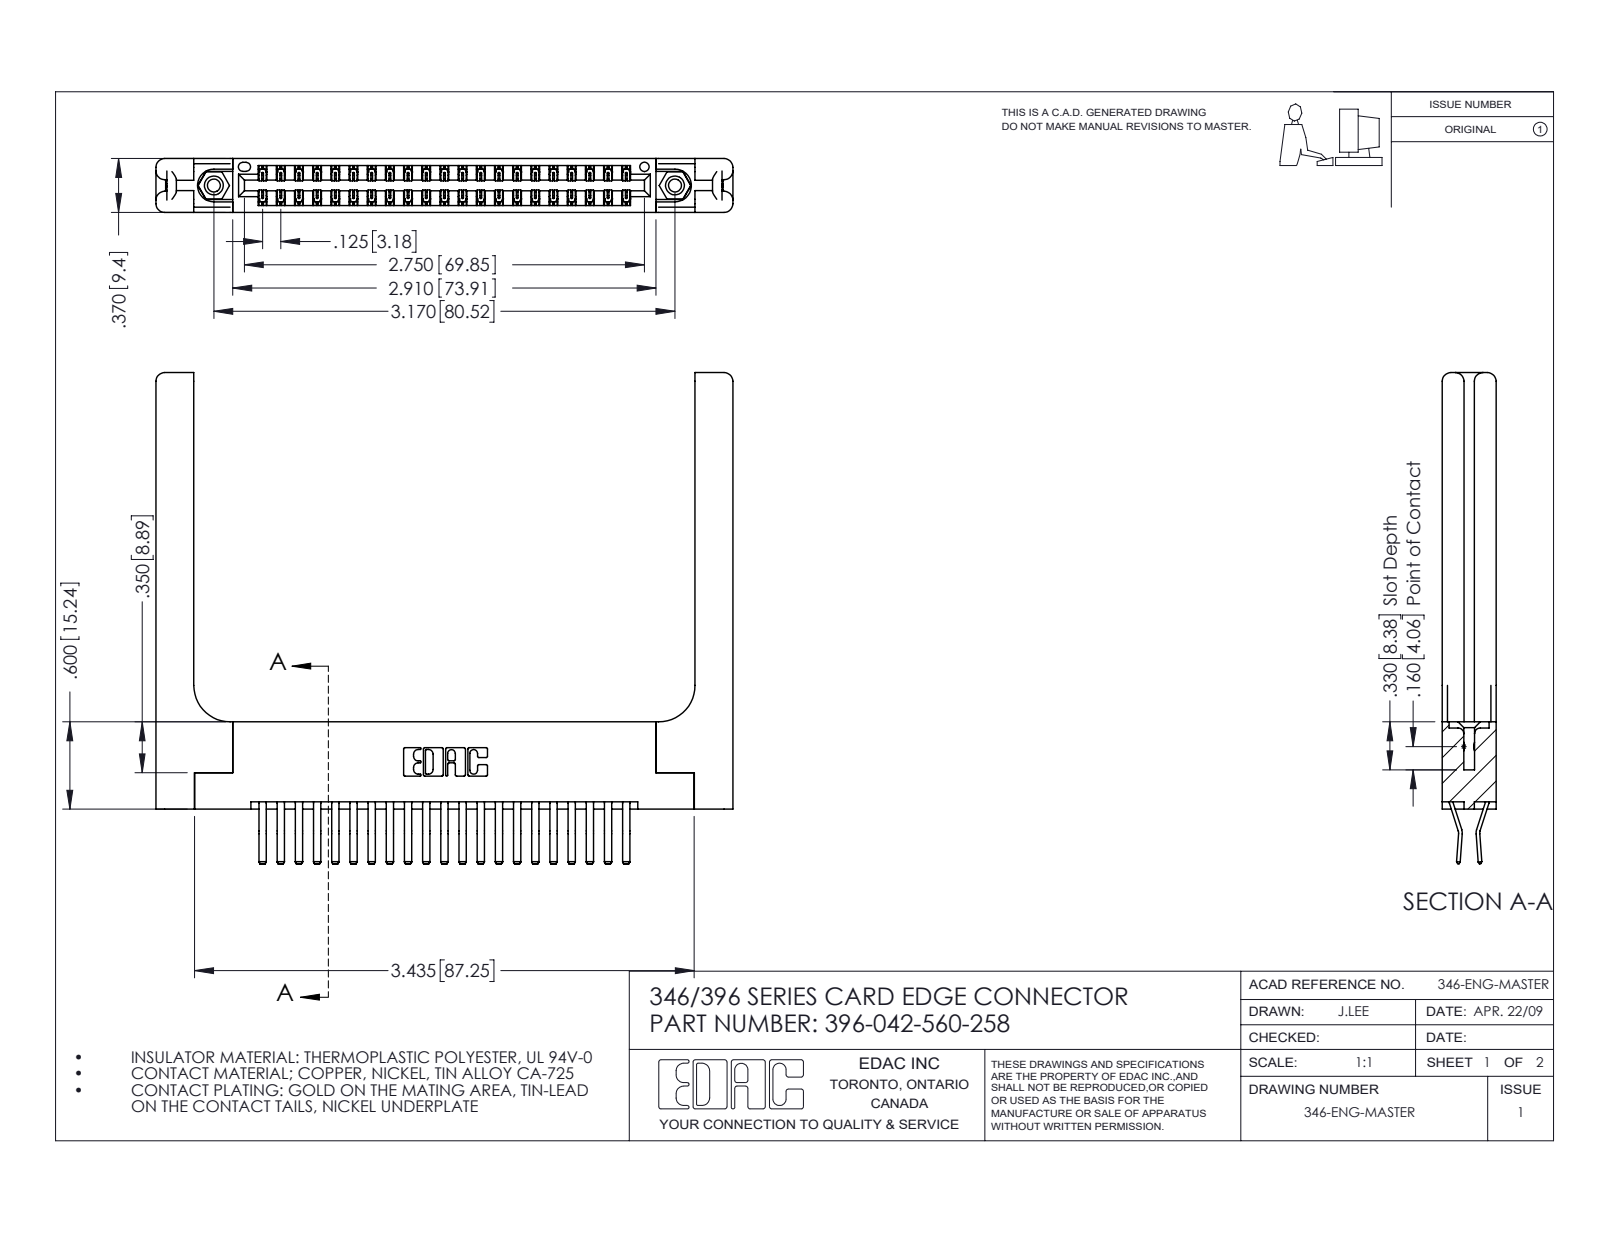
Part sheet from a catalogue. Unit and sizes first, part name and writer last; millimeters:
Units: millimetres
Overall size (bounding box): 100.7 × 85.7 × 9.4
Round holes (diameter × count): ⌀2.3 ×2, ⌀3.2 ×2, ⌀4 ×2, ⌀1.6 ×1
Round bosses / shafts (diameter × count): ⌀3.9 ×2
Partial cylindrical surfaces — rounded edges, fillets, slot ends (radius × count): R0.2 ×63, R0.3 ×22, R1.5 ×16, R0.2 ×6, R0.8 ×6, R0.7 ×3, R0.3 ×2, R0.4 ×2
Main face-to-face distances: 9.4, 1.8, 1.2, 8.2, 3.8, 3.8, 0.6, 6.4, 2, 7.6
Hole centre spacings: 6.2, 75.3, 80.5
Volume: 17 440 mm³ · Surface area: 19 030 mm²
Bodies: 47 solids, 2646 faces (1694 planar, 892 cylindrical, 60 other)
Part name (STEP PRODUCT): 345-292-001_560 Tail; 346-220-058_345-220-058; 346 Part_Flush Mounting Lugs - 0.156 Dia-TH; 345-250-001_345-250-001-102 (+1 more)
STEP written by: SolidWorks 2016 (CONFIG_CONTROL_DESIGN)
